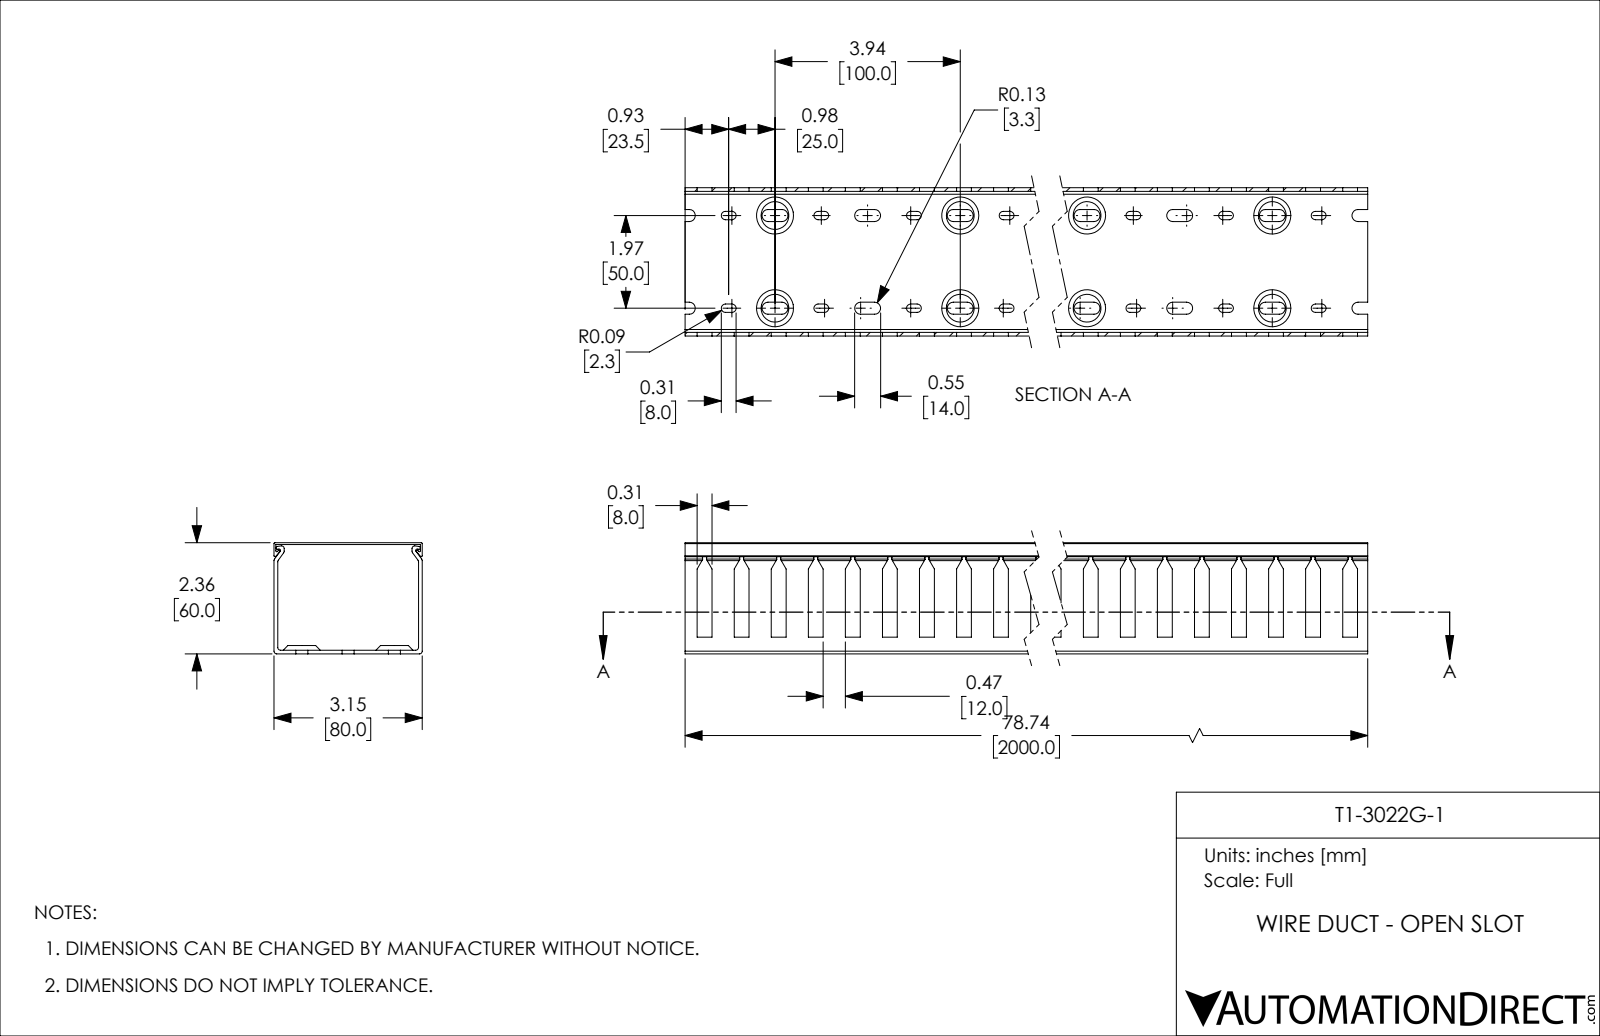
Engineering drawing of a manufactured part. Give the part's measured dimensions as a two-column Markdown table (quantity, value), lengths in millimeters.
| quantity | value |
| --- | --- |
| part name | T1-3022W-1 |
| STEP written by | SolidWorks 2021 (CONFIG_CONTROL_DESIGN) |
| units | millimeters |
| bodies | 2 solids, 1573 faces (762 planar, 731 cylindrical, 80 other) |
| overall size | 2000 × 80 × 60 |
| volume | 970 359 mm³ |
| surface area | 1 168 000 mm² |
| partial cylindrical surfaces (radius × count) | 3.25 × 200, 2.25 × 160, 1.5 × 12, 0.5 × 8, 0.75 × 6 |
| main face-to-face distances | 2, 1, 78, 60, 59, 57, 58, 80, 76, 79 |
